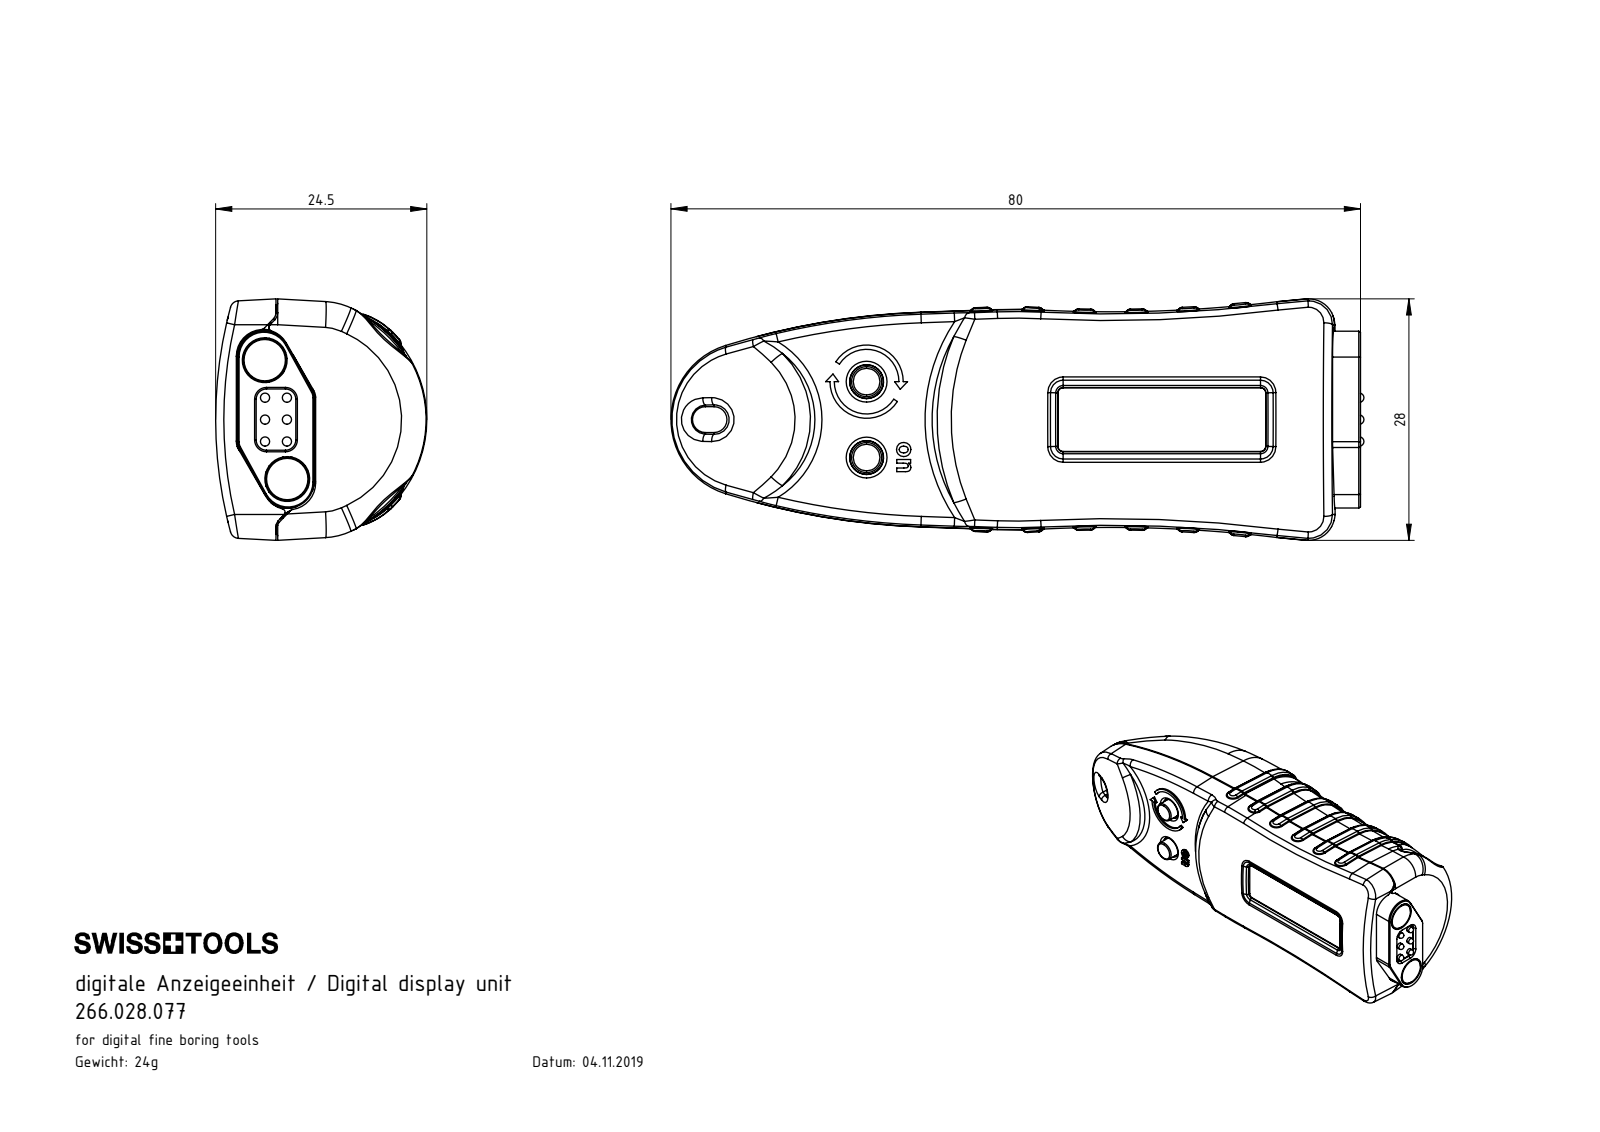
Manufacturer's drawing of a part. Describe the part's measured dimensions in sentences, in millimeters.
The part is named "Dünnglas 0.5+0.1mm; Display-1; 1813-S1-006-10-014101; Schalter (+8 more)". Its 3-D file was written by "SolidWorks 2017 (AUTOMOTIVE_DESIGN)". It is 26 solids with 3004 faces: 578 planar, 479 cylindrical and 1947 other. Overall it measures 80.4 by 28 by 24.5 millimeters. Its volume is 20 759 cubic millimeters and its surface area 23 170 square millimeters. Round holes: 3 of diameter 1.5, 3 of diameter 1.88, 3 of diameter 2, 3 of diameter 2.5, 2 of diameter 5.2, 1 of diameter 0.8, 1 of diameter 7.5. Round bosses or shafts: 6 of diameter 1.38, 6 of diameter 1.07, 6 of diameter 0.8, 3 of diameter 4.8, 3 of diameter 3.2, 3 of diameter 2.25, 3 of diameter 1.51, 3 of diameter 1.4. Partial cylindrical surfaces (rounded edges, fillets, slot ends): 46 of radius 0.4, 41 of radius 0.5, 38 of radius 0.1, 33 of radius 0.2, 30 of radius 0.3, 27 of radius 0.14, 26 of radius 0.6, 9 of radius 0.14. The main face-to-face distances are 1.55, 0.5, 1, 1.1, 0.6, 3.4, 6.27, 4.72, 5, 4.4. The hole center spacings are 4.32, 15.23, 57.72, 58.16, 62.85, 63.34, 5.2, 9.13.
